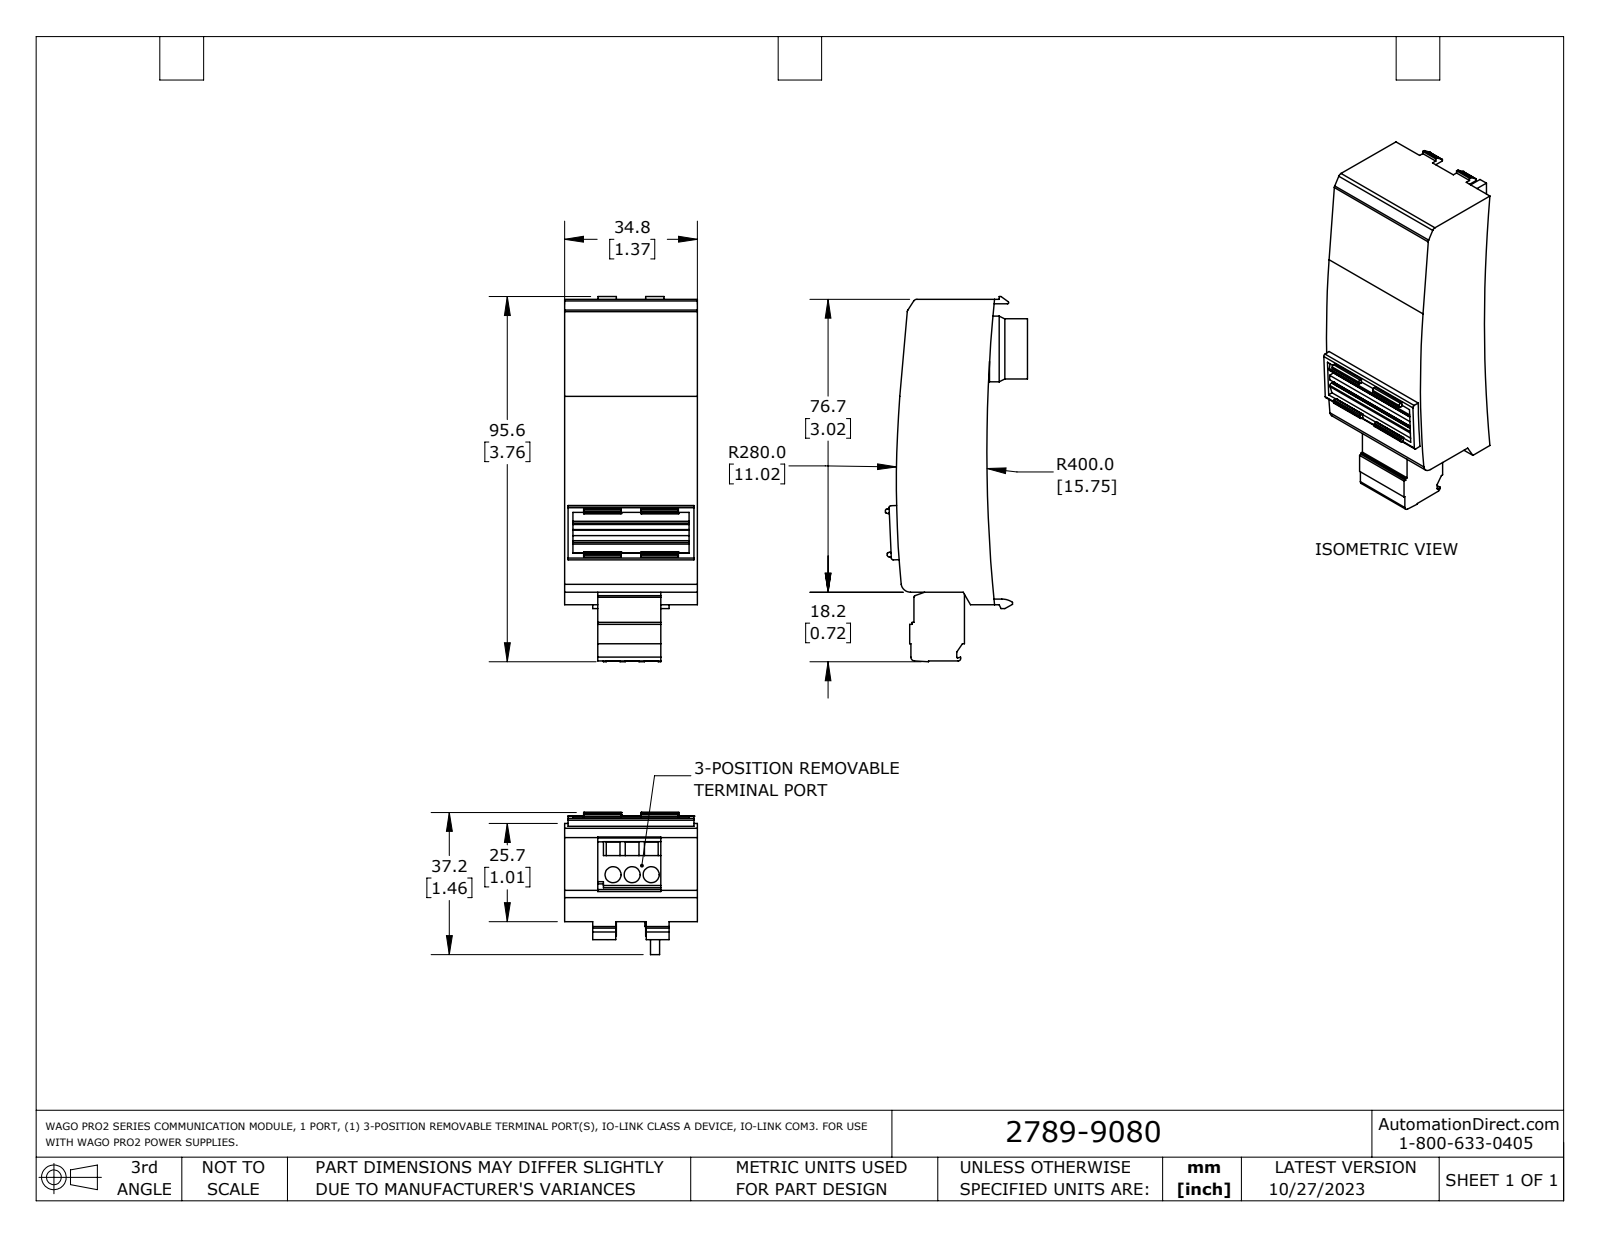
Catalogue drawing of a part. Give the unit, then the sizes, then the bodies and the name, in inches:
Units: inches
Overall size (bounding box): 3.76 × 1.507 × 1.439
Round holes (diameter × count): ⌀0.165 ×3
Partial cylindrical surfaces — rounded edges, fillets, slot ends (radius × count): R0.008 ×8, R0.012 ×6, R0.02 ×6, R0.039 ×3, R0.017 ×2, R0.024 ×2, R0.197 ×2, R0.016 ×1
Main face-to-face distances: 1.37, 3.021, 0.992, 0.65, 0.343, 0.378, 1.028, 0.13, 3.151, 0.52
Hole centre spacings: 0.197, 0.394
Volume: 4.165 in³ · Surface area: 20.41 in²
Bodies: 1 solid, 171 faces (132 planar, 39 cylindrical, 0 other)
Part name (STEP PRODUCT): 2789-9080
STEP written by: SolidWorks 2023 (AUTOMOTIVE_DESIGN)
